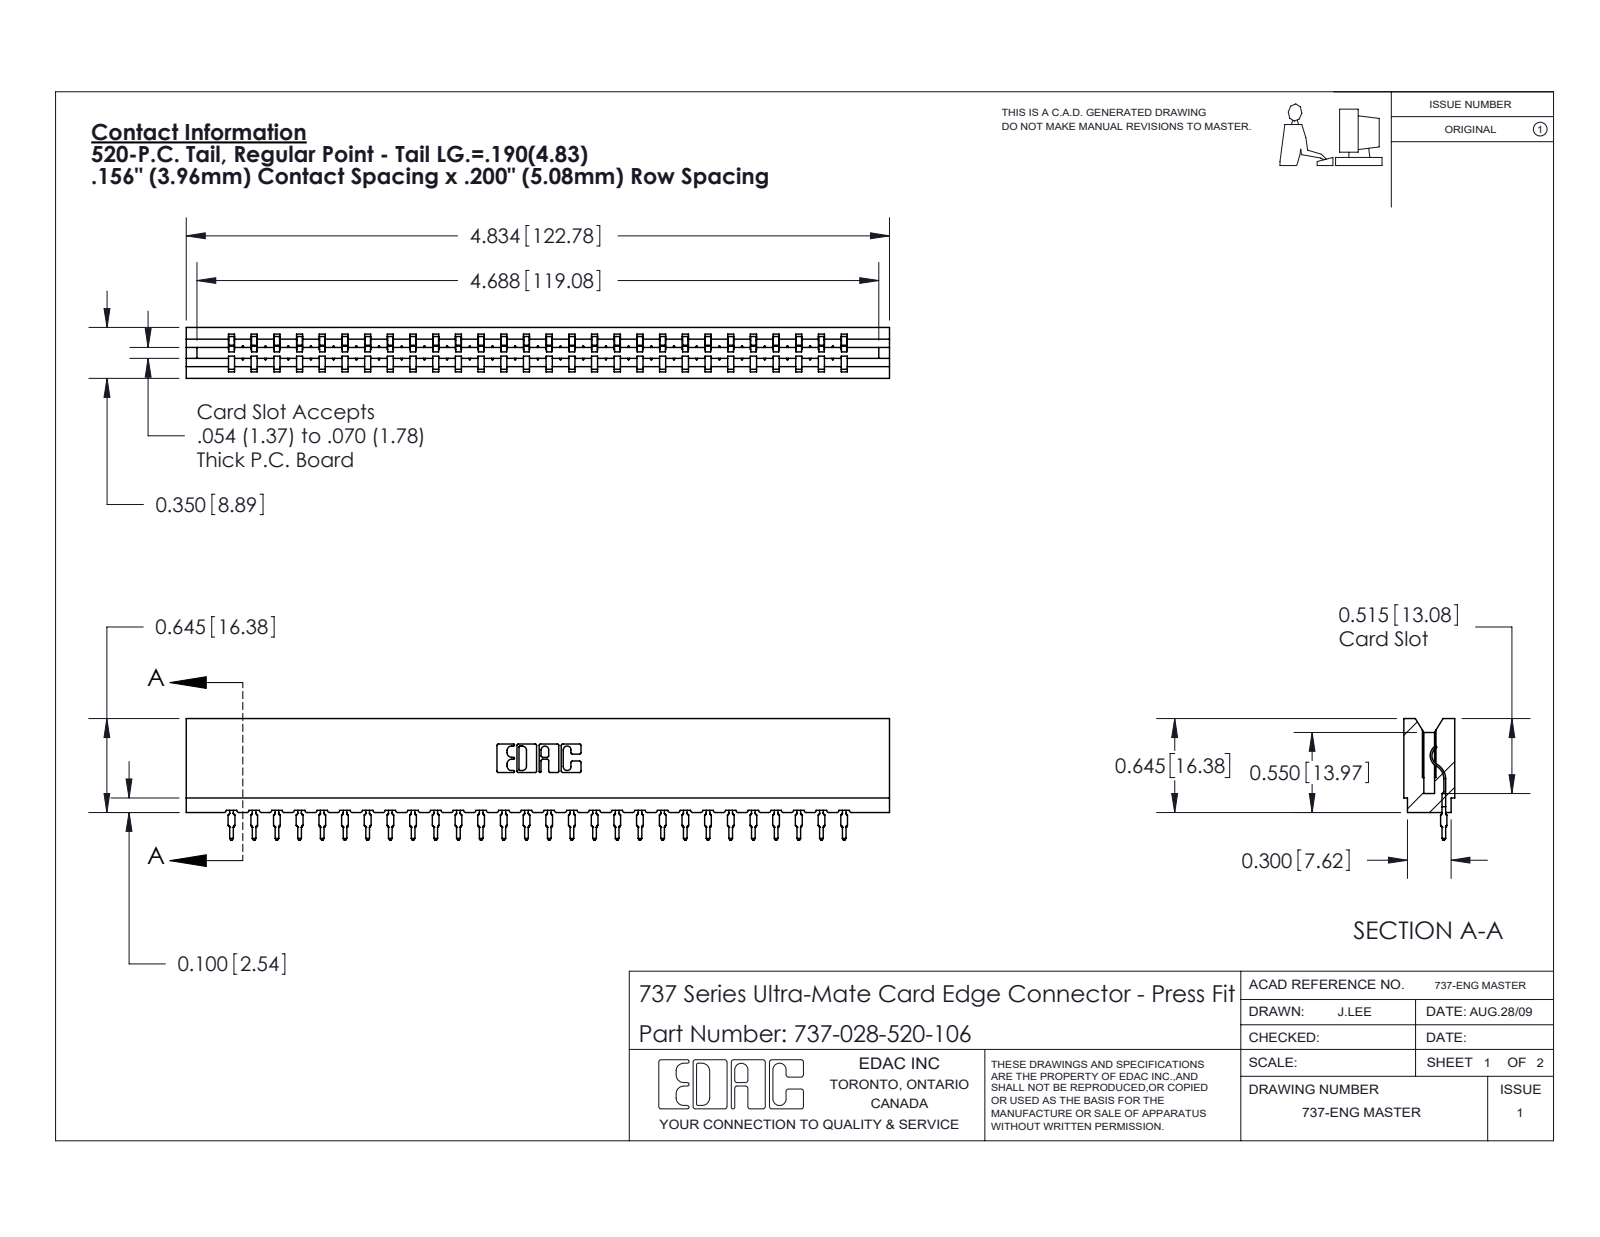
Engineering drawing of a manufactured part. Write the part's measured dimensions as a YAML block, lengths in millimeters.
part_name: "745-292-001_520; 737 Part_Insulator Option - 06; 737-028-520-106"
step_written_by: "SolidWorks 2020 (CONFIG_CONTROL_DESIGN)"
units: millimeters
bodies: {solids: 29, faces: 3259, planar: 1959, cylindrical: 572, other: 728}
overall_size: [122.8, 21.2, 8.9]
volume: 11900
surface_area: 15550
partial_cylinders:
  - {radius: 0.4, count: 56}
  - {radius: 0.5, count: 56}
  - {radius: 0.3, count: 22}
  - {radius: 0.2, count: 6}
  - {radius: 0.8, count: 6}
  - {radius: 0.1, count: 4}
  - {radius: 0.3, count: 4}
  - {radius: 0.7, count: 3}
face_to_face_distances: [3.5, 5.4, 8.9, 1.9, 4, 1.1, 7.7, 2.4, 4.2, 15.8]
